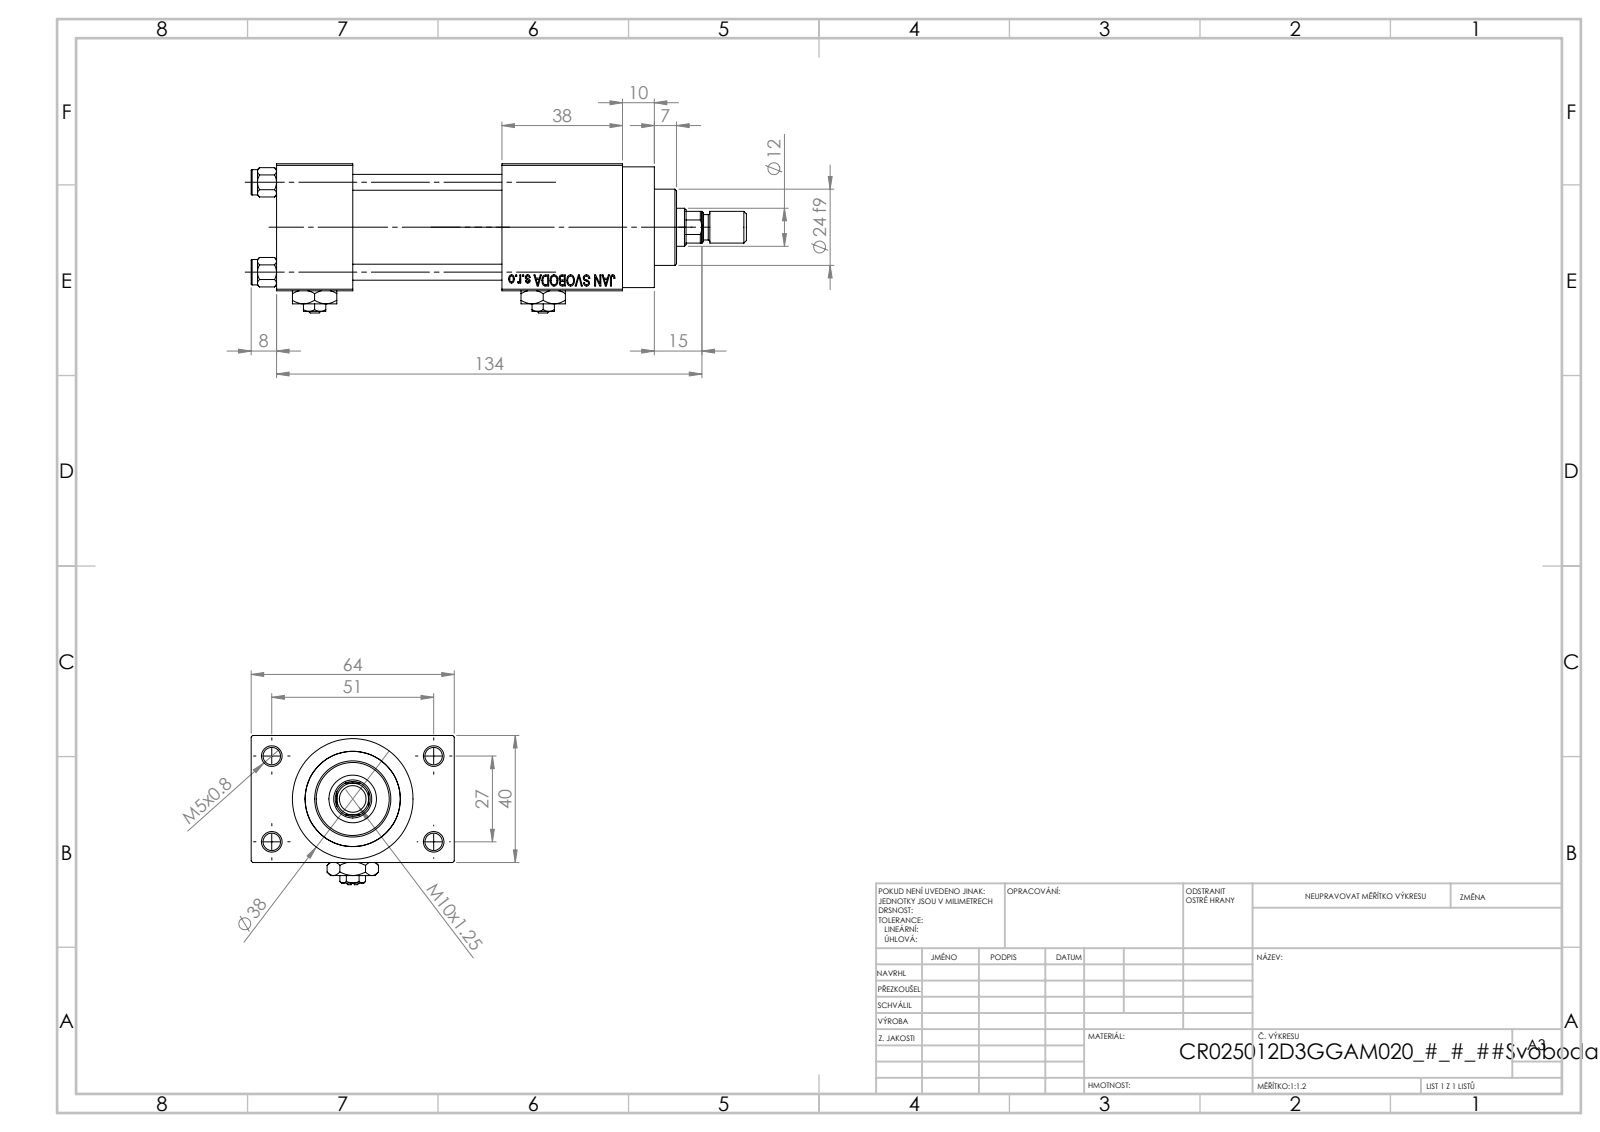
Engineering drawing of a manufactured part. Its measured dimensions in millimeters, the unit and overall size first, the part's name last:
Units: millimetres
Overall size (bounding box): 156 × 64 × 47
Round holes (diameter × count): ⌀5 ×4, ⌀5.5 ×4, ⌀20 ×3, ⌀7 ×2, ⌀13.16 ×2, ⌀6.5 ×1, ⌀12 ×1, ⌀15 ×1, ⌀25 ×1, ⌀30 ×1
Round bosses / shafts (diameter × count): ⌀8 ×5, ⌀38 ×1, ⌀31 ×1, ⌀24 ×1, ⌀10 ×1
Partial cylindrical surfaces — rounded edges, fillets, slot ends (radius × count): R5.5 ×1
Main face-to-face distances: 40, 52, 12, 47, 71, 24, 64, 38, 85, 109
Hole centre spacings: 11.37, 20.01, 28.3, 28.85, 29.89, 39.66, 48.34, 27
Volume: 175 245 mm³ · Surface area: 63 925 mm²
Bodies: 14 solids, 1216 faces (546 planar, 104 cylindrical, 566 other)
Part name (STEP PRODUCT): V215CR_D_TYCINKA; V215_VC_A; V215CR_D_Body; V215CR_VCP_D (+3 more)
STEP written by: SolidWorks 2019 (CONFIG_CONTROL_DESIGN)
